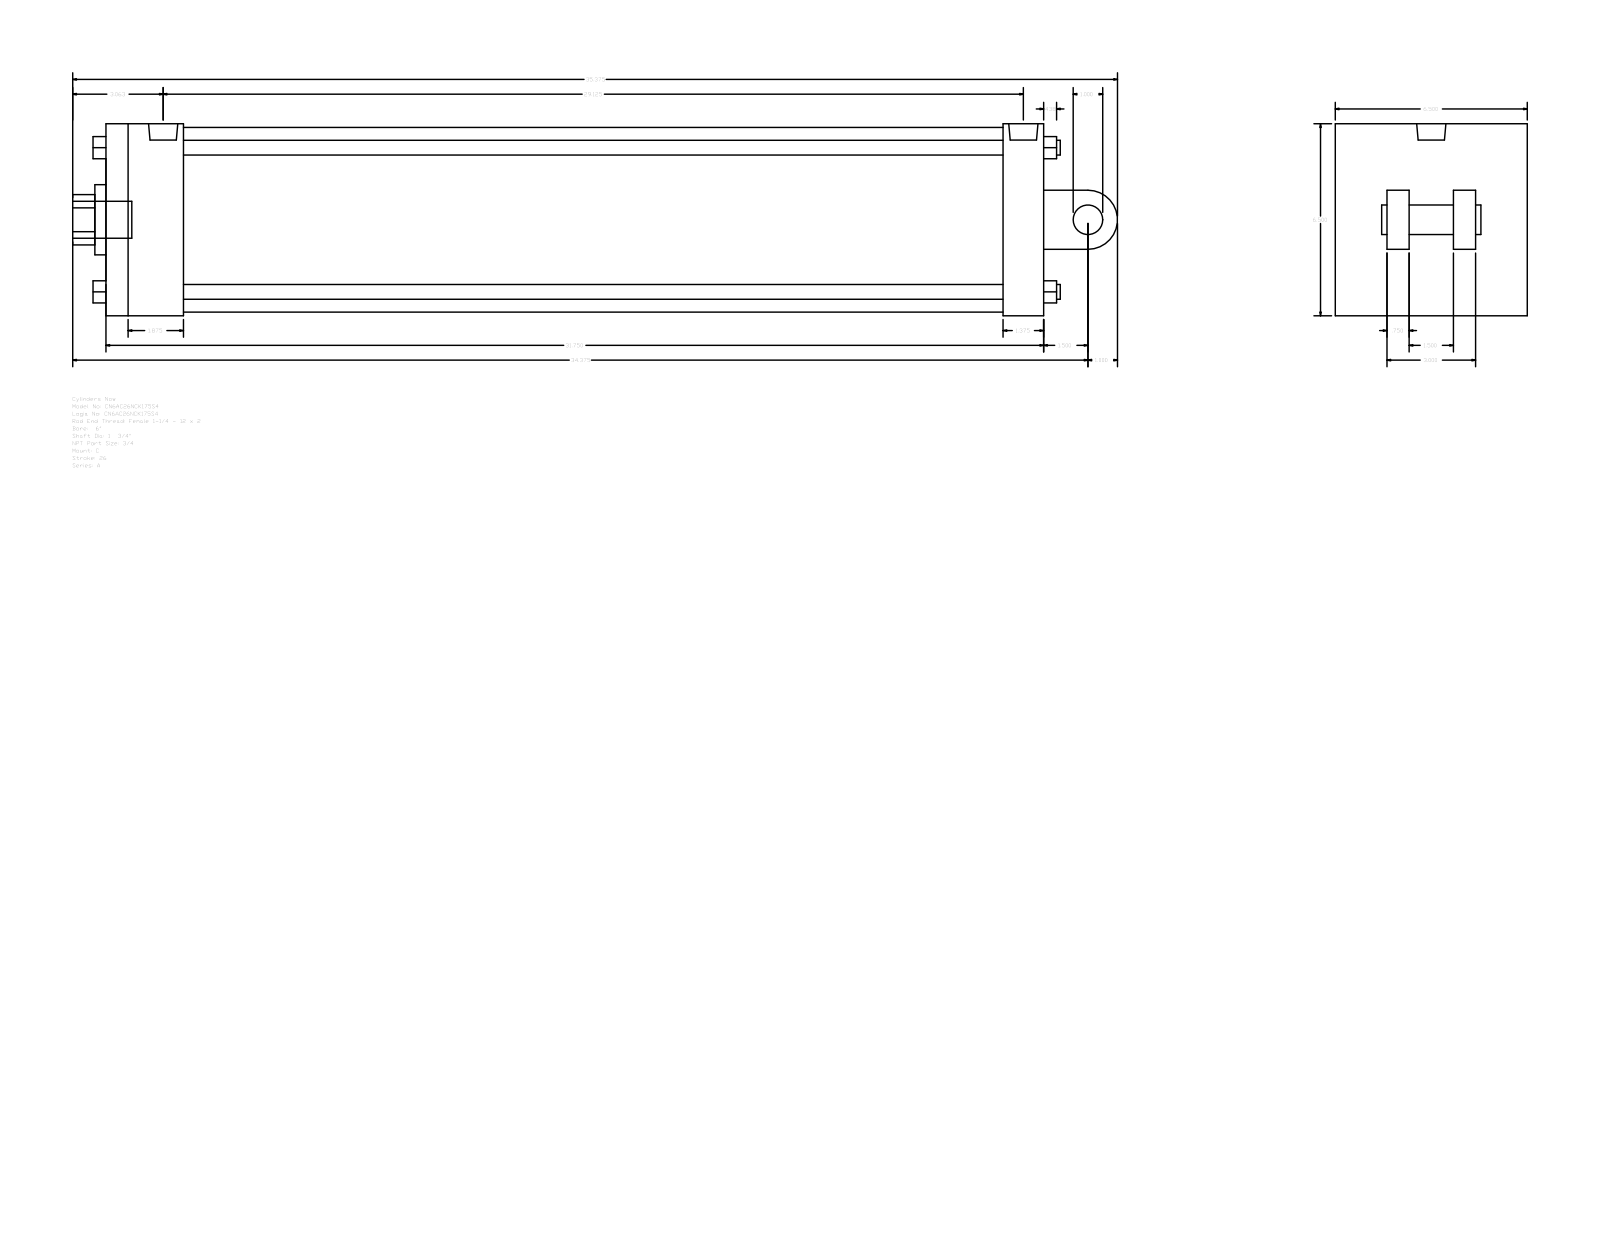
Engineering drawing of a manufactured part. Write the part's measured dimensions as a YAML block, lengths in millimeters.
part_name: "A_C__0600_1.75"
step_written_by: "GSSL Pune (CONFIG_CONTROL_DESIGN)"
units: millimeters
bodies: {solids: 0, faces: 135, planar: 102, cylindrical: 33, other: 0}
overall_size: [898.52, 165.1, 165.1]
round_holes:
  - {diameter: 15.08, count: 2}
  - {diameter: 25.12, count: 1}
  - {diameter: 44.45, count: 1}
  - {diameter: 60.33, count: 1}
  - {diameter: 158.75, count: 1}
round_bosses_or_shafts:
  - {diameter: 12.7, count: 4}
  - {diameter: 15.08, count: 2}
  - {diameter: 31.75, count: 1}
  - {diameter: 25.4, count: 1}
  - {diameter: 25.12, count: 1}
partial_cylinders:
  - {radius: 21.63, count: 1}
  - {radius: 25.4, count: 1}
face_to_face_distances: [165.1, 806.45, 19.05, 57.15, 34.92, 66.68, 739.77, 771.53, 704.85, 44.45]
hole_center_spacings: [5.56]
